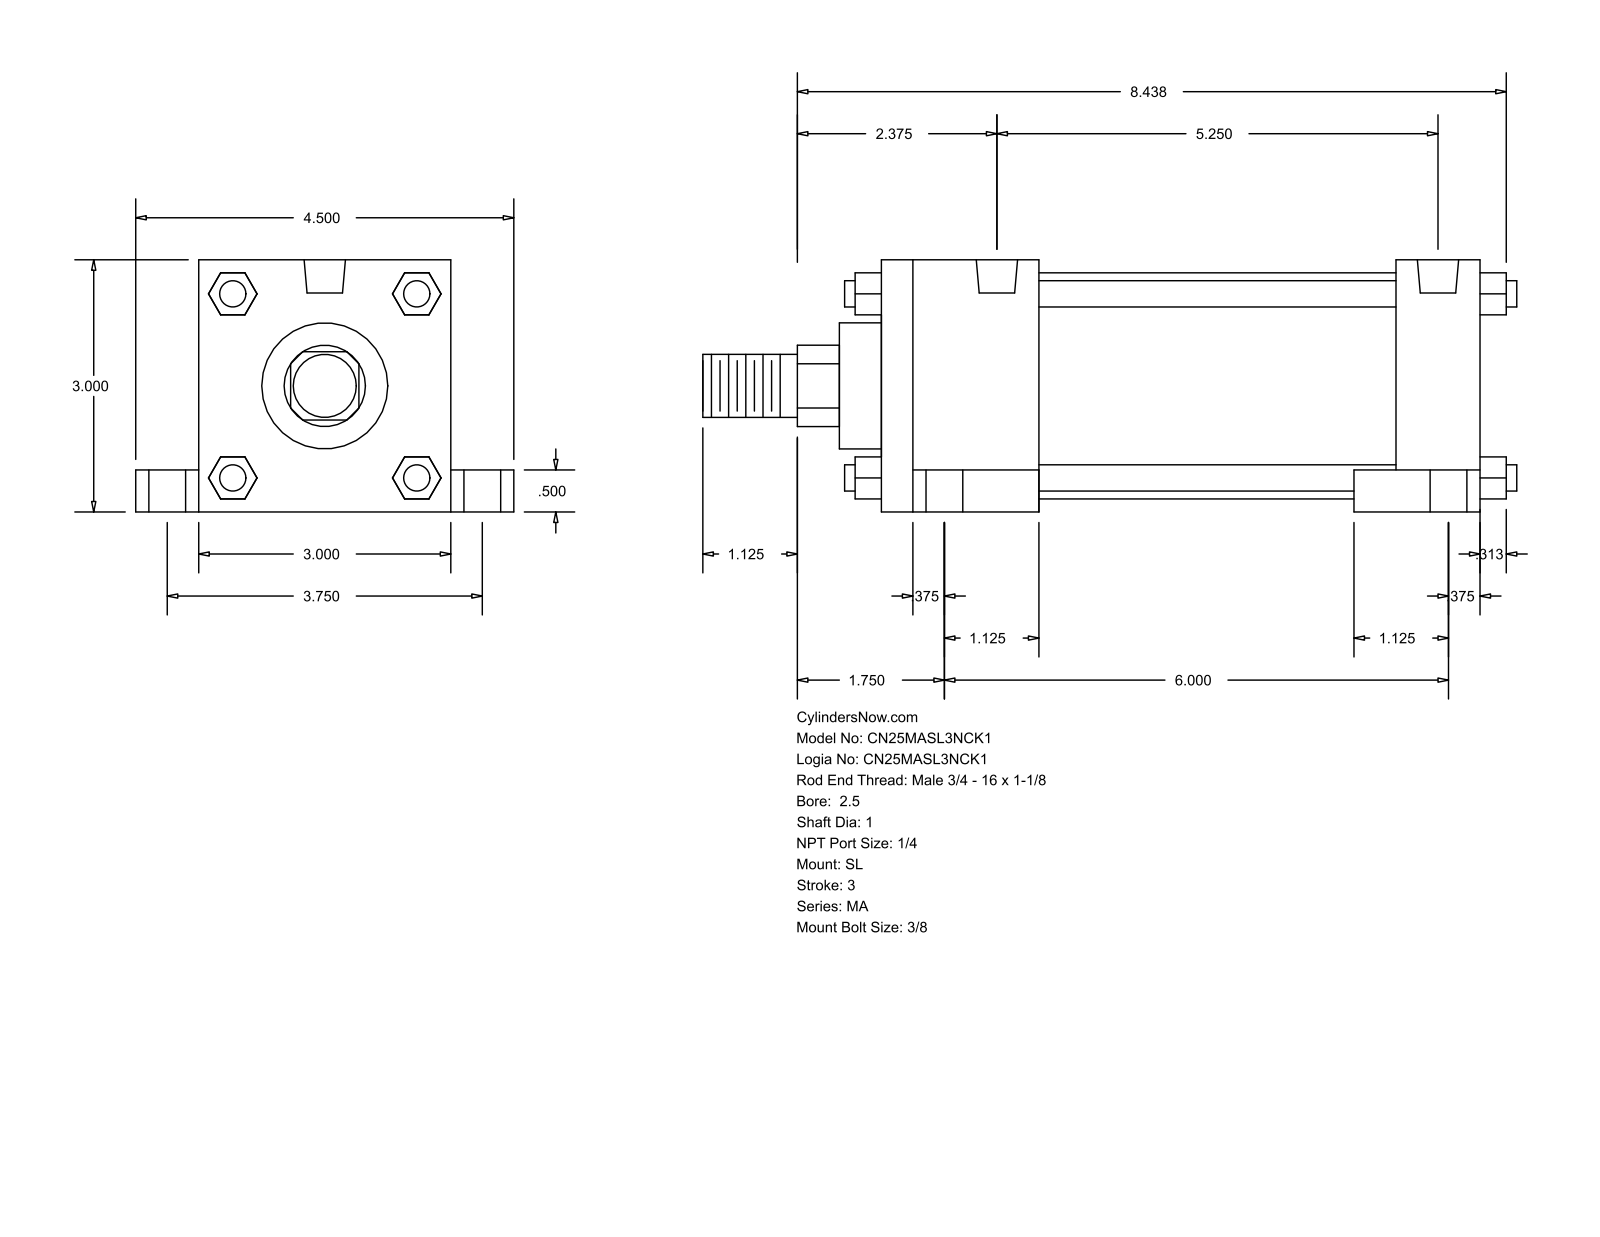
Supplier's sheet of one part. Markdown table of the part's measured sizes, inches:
| quantity | value |
| --- | --- |
| part name | MA_SL__0250_1 |
| STEP written by | GSSL Pune (CONFIG_CONTROL_DESIGN) |
| units | inches |
| bodies | 0 solids, 148 faces (112 planar, 36 cylindrical, 0 other) |
| overall size | 9.687 × 4.5 × 3 |
| round holes (diameter × count) | 0.313 × 4, 0.437 × 4, 0.687 × 4, 0.492 × 2 |
| round bosses / shafts (diameter × count) | 0.313 × 4, 2.69 × 1, 1.5 × 1, 1 × 1, 0.75 × 1 |
| partial cylindrical surfaces (radius × count) | 0.484 × 1 |
| main face-to-face distances | 3, 7.125, 0.5, 1.875, 5.25, 6.125, 4.25, 1, 0.75, 3.75 |
| hole center spacings | 1.879, 1.976, 3.75, 5.25, 5.693, 6, 6.167, 7.075 |
